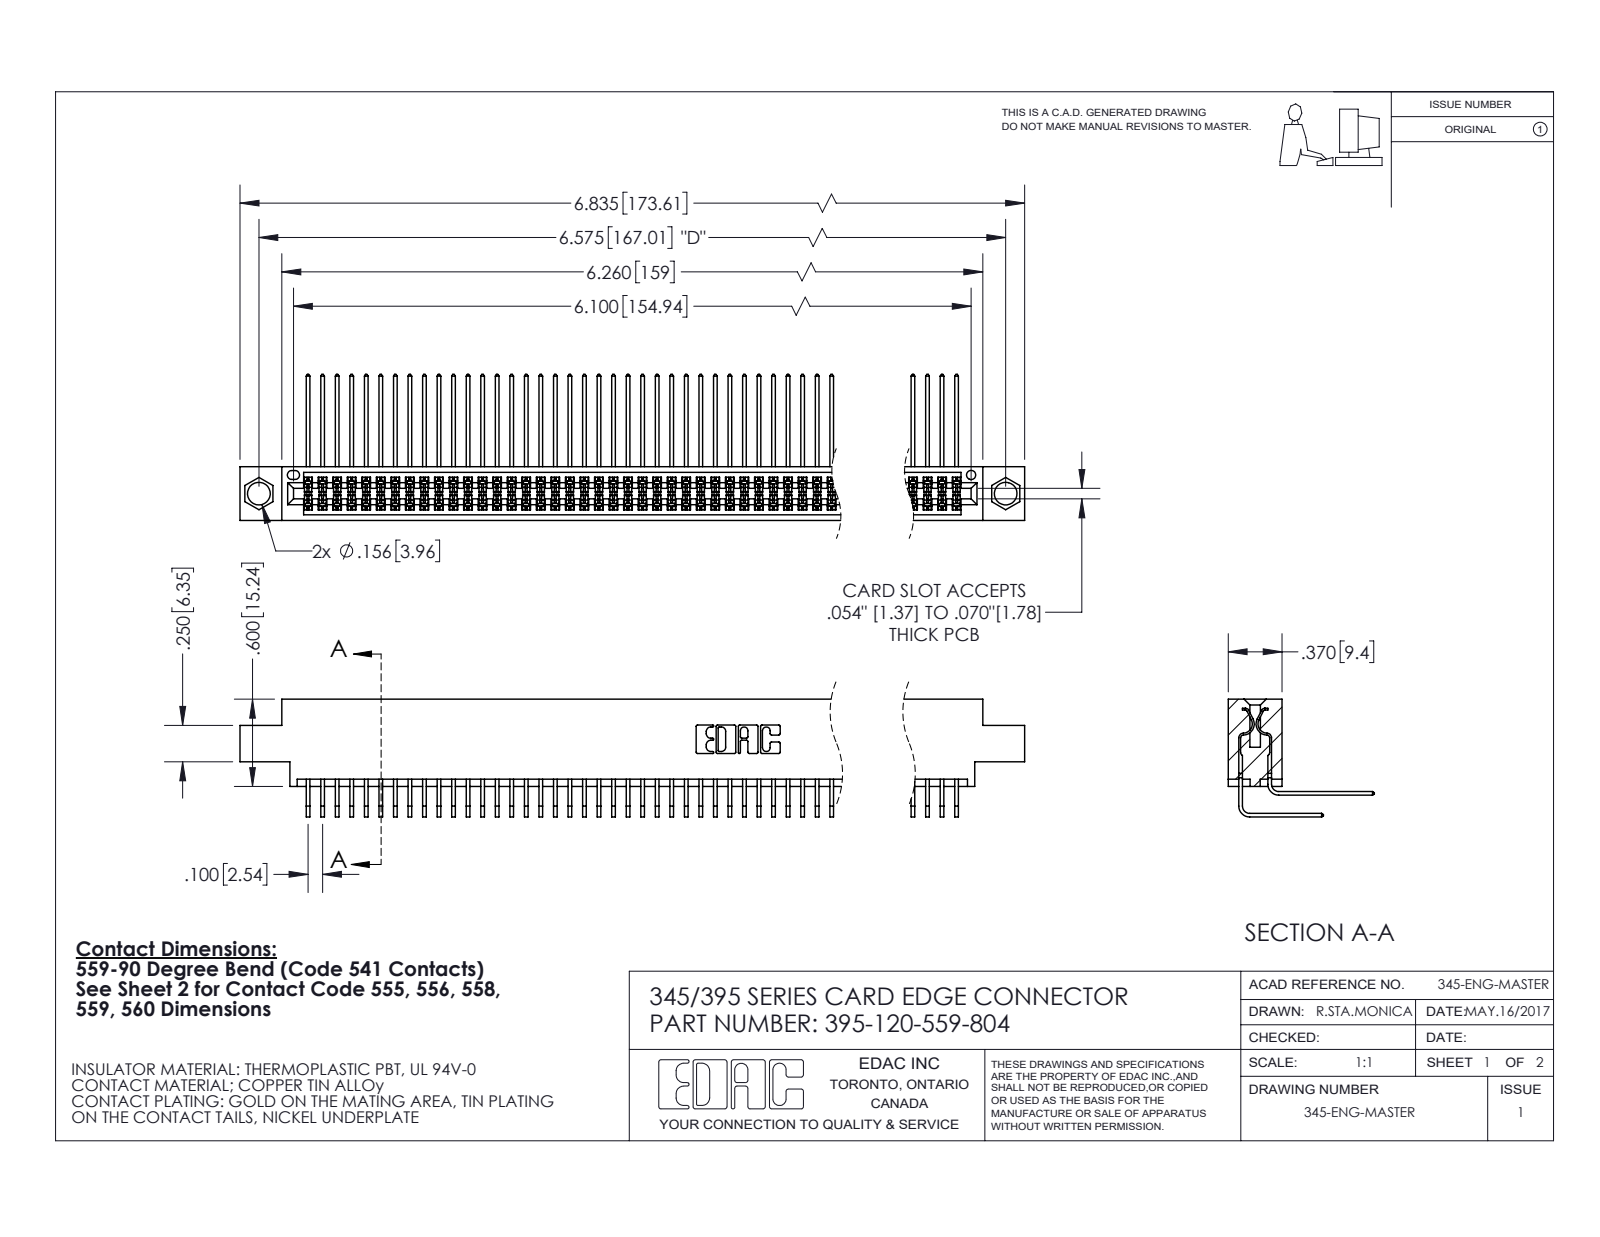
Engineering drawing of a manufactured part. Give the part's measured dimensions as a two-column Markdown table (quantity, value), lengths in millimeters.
| quantity | value |
| --- | --- |
| part name | 345-292-001_559 Tail - 2; 395-120-559-804; 345 Part_0.170 Offset - 0.156 Dia-TI; 345-292-001_558 559 Tail - 1 |
| STEP written by | SolidWorks 2020 (CONFIG_CONTROL_DESIGN) |
| units | millimeters |
| bodies | 121 solids, 6384 faces (4298 planar, 2086 cylindrical, 0 other) |
| overall size | 173.6 × 25.5 × 20.5 |
| volume | 17 500 mm³ |
| surface area | 29 470 mm² |
| round holes (diameter × count) | 4 × 2, 1.6 × 1 |
| partial cylindrical surfaces (radius × count) | 0.2 × 180, 0.3 × 22, 0.2 × 6, 0.8 × 6, 0.7 × 3, 0.4 × 2, 0.5 × 2, 0.6 × 2 |
| main face-to-face distances | 1.8, 7.6, 9.4, 5.1, 2.5, 6.9, 0.6, 5.7, 4.4, 3.8 |
| hole center spacings | 6.9, 161, 167 |
